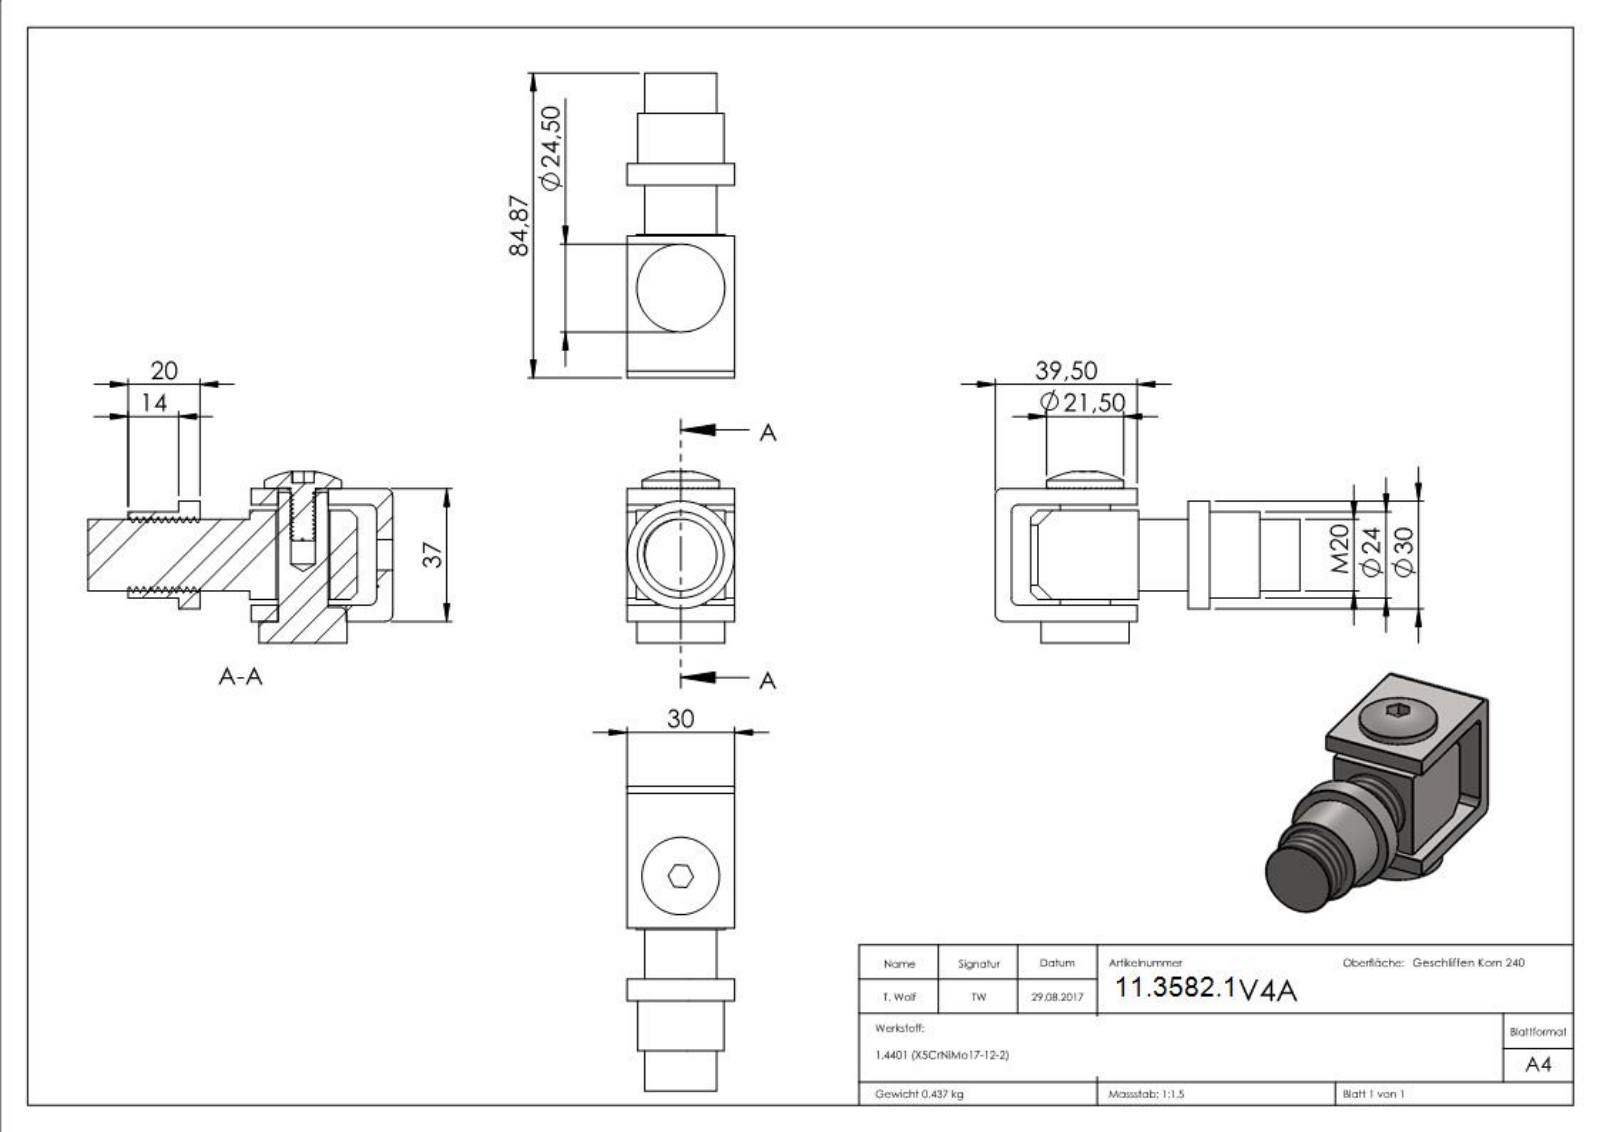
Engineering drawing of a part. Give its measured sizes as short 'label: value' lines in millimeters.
name: 120-M20-V4A Teil 2; 120-M20-V4A Teil4; 120-M20-V4A Teil1_120-M20-V4A Teil 1; 120-M20-V4A Teil1 (+3 more)
written by: SolidWorks 2018 (CONFIG_CONTROL_DESIGN)
unit: mm
bodies: 5 solids, 669 faces (482 planar, 28 cylindrical, 159 other)
size: 84.87 × 47.75 × 30
volume: 54 619 mm³; area: 24 878 mm²
holes: 1× ⌀6.8, 1× ⌀8.5, 1× ⌀14, 1× ⌀15, 1× ⌀18
bosses: 1× ⌀30, 1× ⌀24.5, 1× ⌀24, 1× ⌀21.5, 1× ⌀20, 1× ⌀7
rounds: 4× R2
face distances: 4.5, 32.5, 24.8, 37, 26.4, 6.1, 30.9, 1.6, 2.6, 27.4
